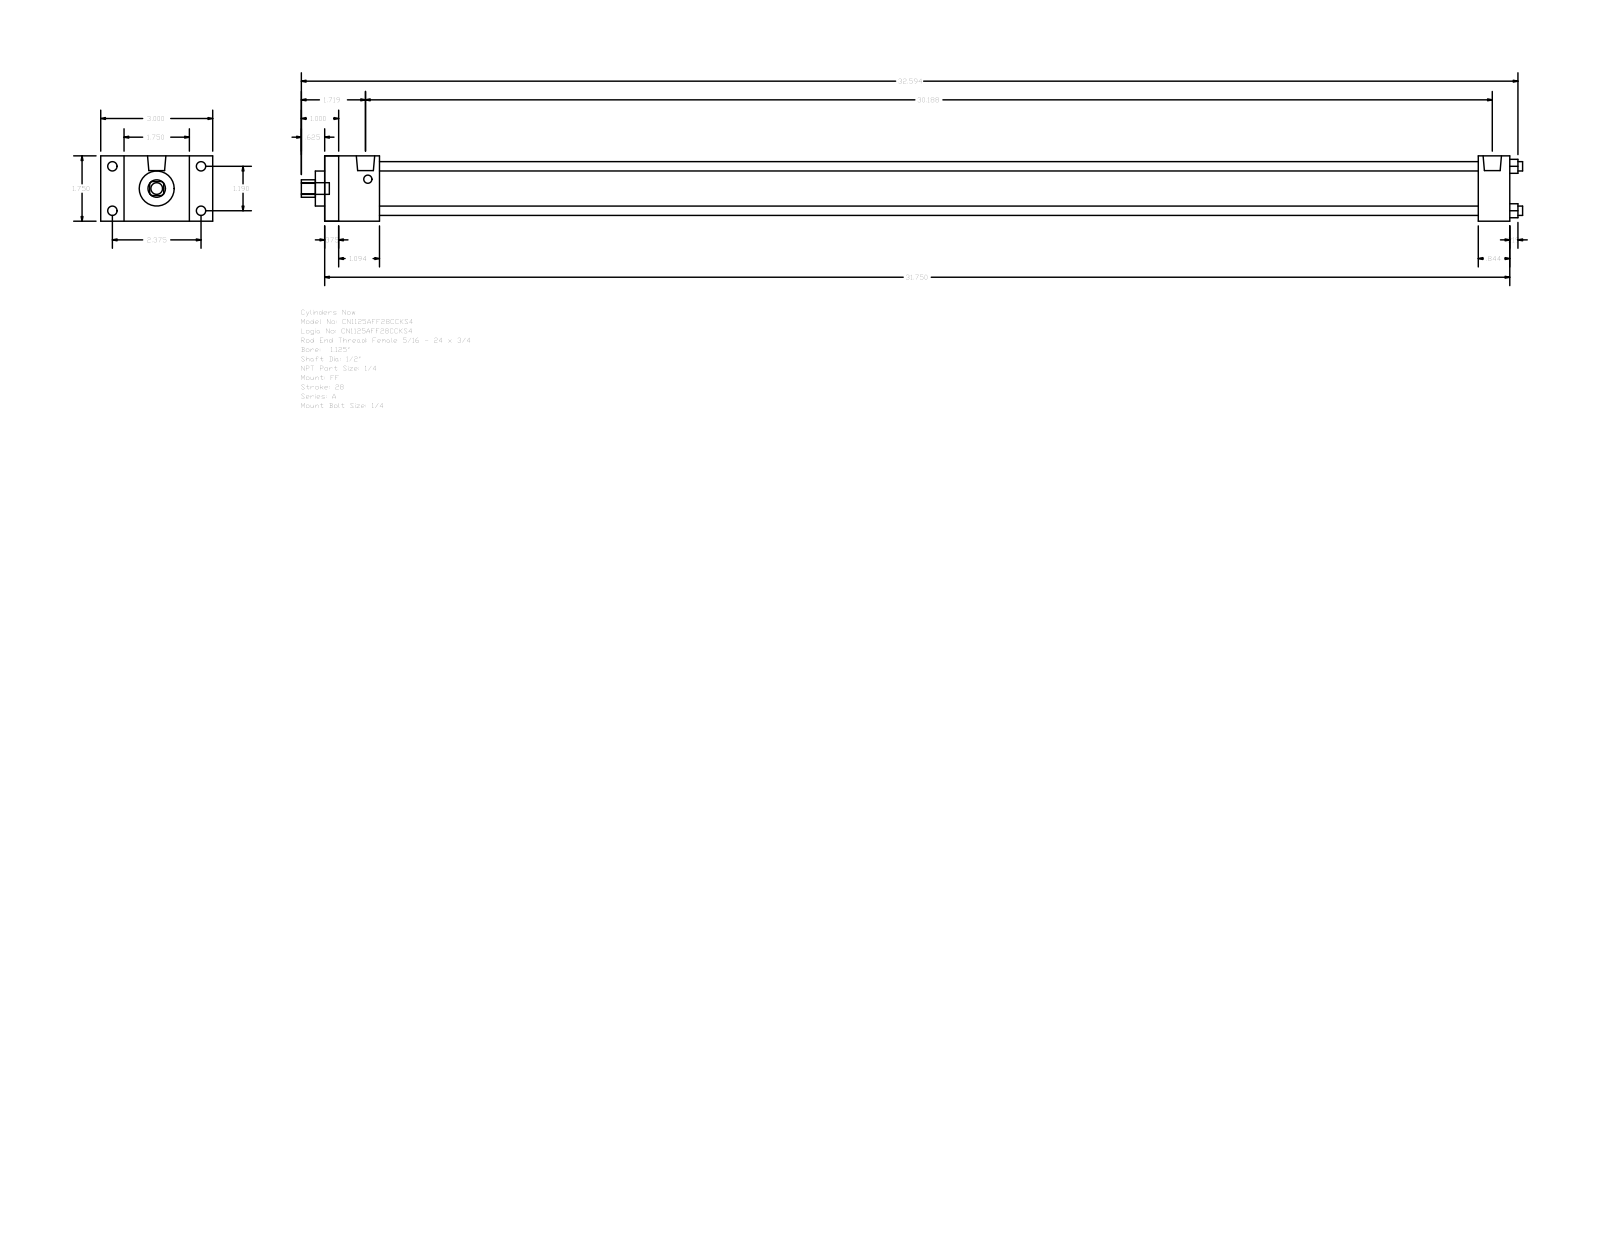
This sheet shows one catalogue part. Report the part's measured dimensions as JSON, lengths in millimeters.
{"part_name": "A_FF__0112_0.5", "step_written_by": "GSSL Pune (CONFIG_CONTROL_DESIGN)", "units": "millimeters", "bodies": {"solids": 0, "faces": 92, "planar": 64, "cylindrical": 28, "other": 0}, "overall_size": [831.06, 76.2, 44.45], "round_holes": [[6.35, 4], [12.7, 1], [23.81, 1], [31.88, 1]], "round_bosses_or_shafts": [[6.35, 4], [5.56, 4], [12.49, 2], [7.94, 1]], "partial_cylinders_radius": [[5.94, 1]], "face_to_face_distances": [44.46, 806.45, 9.52, 796.93, 15.87, 785.01, 775.49, 21.44, 37.3, 27.78], "hole_center_spacings": [21.37, 30.22, 42.74]}
